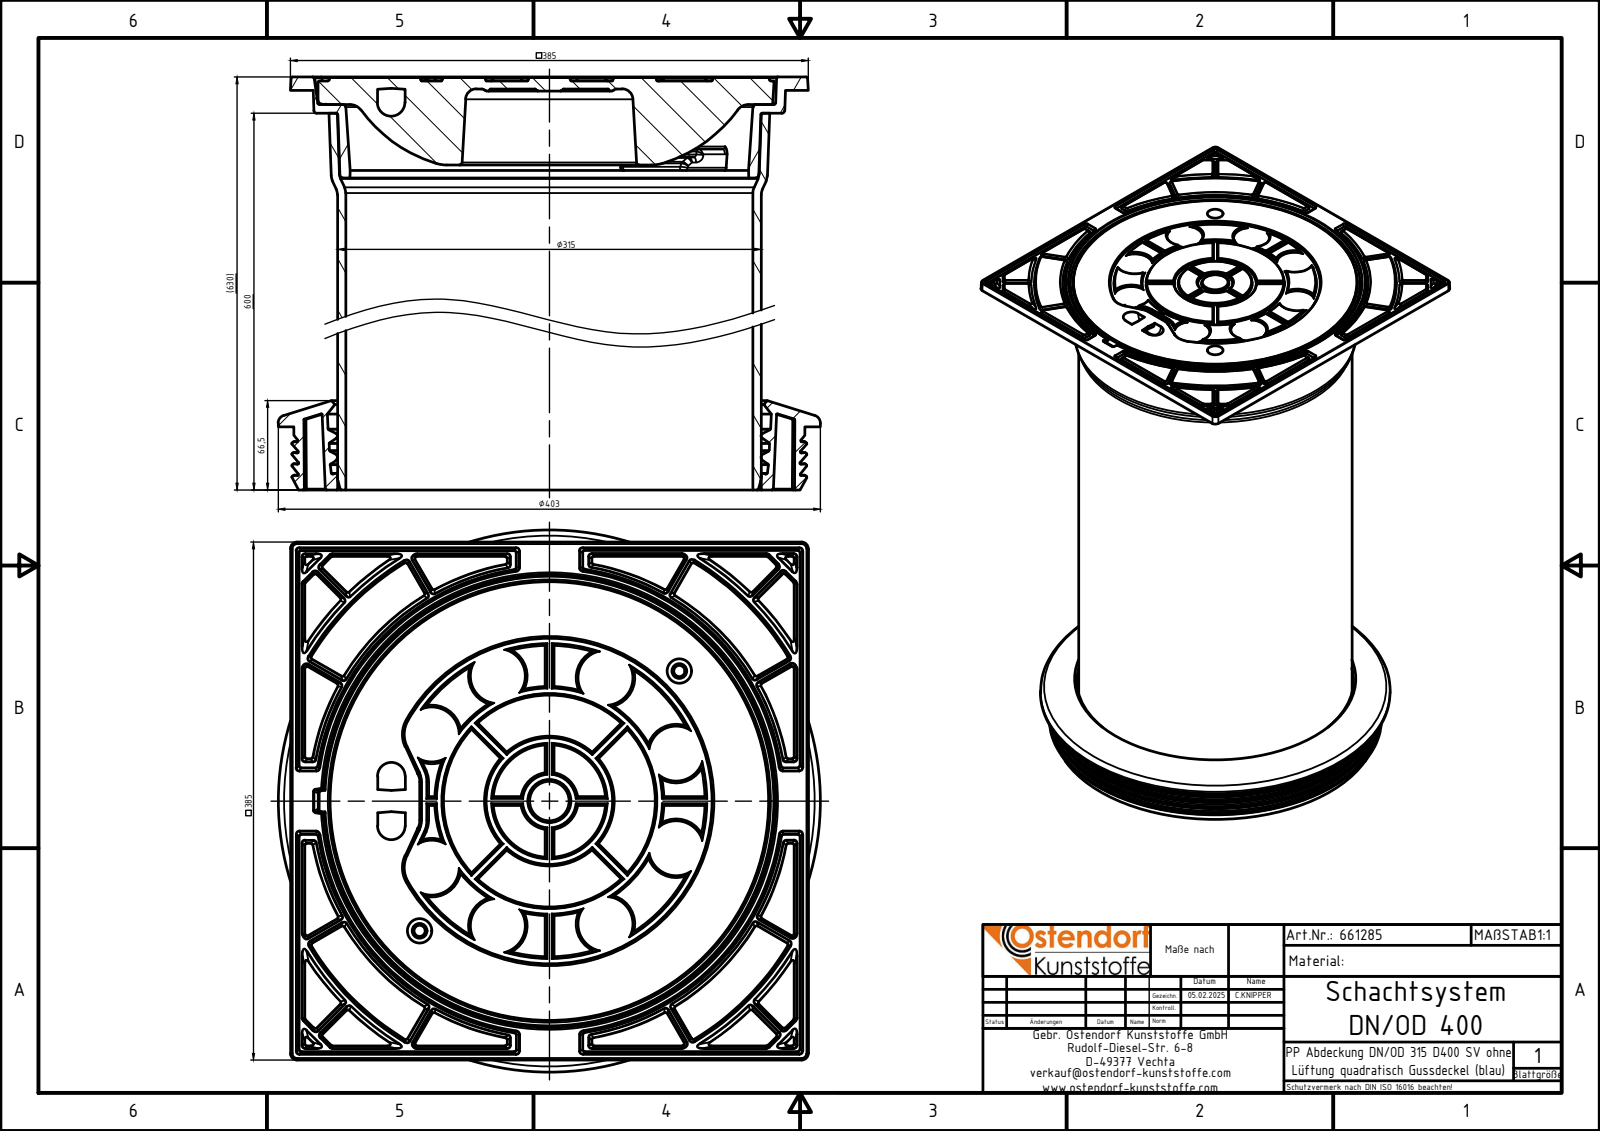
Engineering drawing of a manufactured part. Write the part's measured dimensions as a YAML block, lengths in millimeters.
part_name: "661285z; 660300z; 660500_05.02.25z; 990055z (+1 more)"
step_written_by: "Autodesk Inventor 2024 (AUTOMOTIVE_DESIGN)"
units: millimeters
bodies: {solids: 4, faces: 1769, planar: 241, cylindrical: 355, other: 1173}
overall_size: [627, 403, 403]
volume: 9089000
surface_area: 2128000
round_holes:
  - {diameter: 8.38, count: 2}
  - {diameter: 11, count: 2}
  - {diameter: 18, count: 2}
  - {diameter: 302.6, count: 1}
  - {diameter: 315, count: 1}
round_bosses_or_shafts:
  - {diameter: 403, count: 1}
  - {diameter: 380, count: 1}
partial_cylinders:
  - {radius: 1, count: 204}
  - {radius: 2.5, count: 48}
  - {radius: 0.5, count: 14}
  - {radius: 4, count: 8}
  - {radius: 2, count: 4}
  - {radius: 3, count: 1}
face_to_face_distances: [9.5, 0.5, 10, 10.5, 20.5, 20, 6.5, 2.5, 17, 26.5]
hole_center_spacings: [136.5, 136.51, 273.01]
